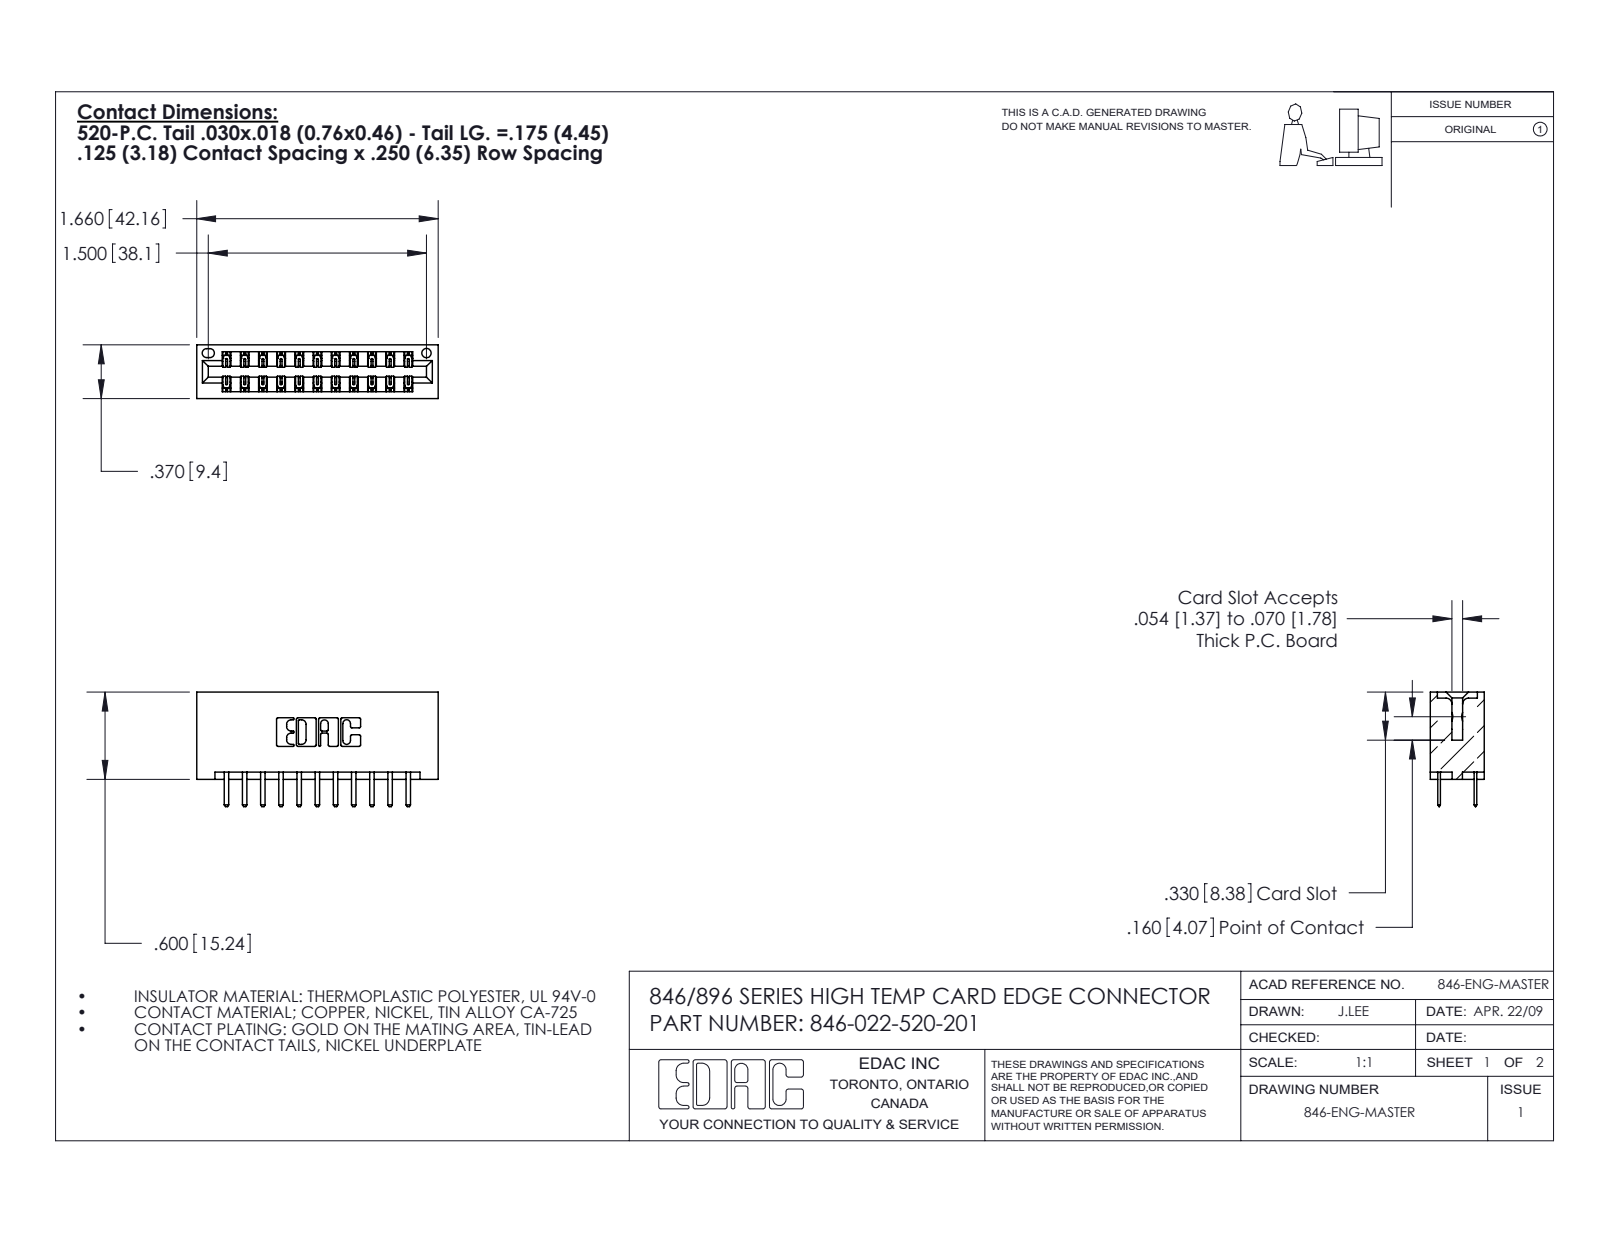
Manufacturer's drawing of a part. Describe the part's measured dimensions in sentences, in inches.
The part is named "346 Part_No Mounting Lugs; 346-022-520-201; 345-292-001_345-293-120". Its 3-D file was written by "SolidWorks 2016 (CONFIG_CONTROL_DESIGN)". It is 14 solids with 896 faces: 598 planar, 298 cylindrical and 0 other. Overall it measures 1.66 by 0.788 by 0.37 inches. Its volume is 0.266 cubic inches and its surface area 8.037 square inches. Round holes: 1 of diameter 0.064. Partial cylindrical surfaces (rounded edges, fillets, slot ends): 26 of radius 0.01, 24 of radius 0.006, 22 of radius 0.01, 6 of radius 0.007, 6 of radius 0.031, 3 of radius 0.026, 2 of radius 0.014, 2 of radius 0.022. The main face-to-face distances are 0.25, 0.048, 0.322, 0.37, 0.148, 0.222, 0.1, 0.174, 0.5, 0.072.
